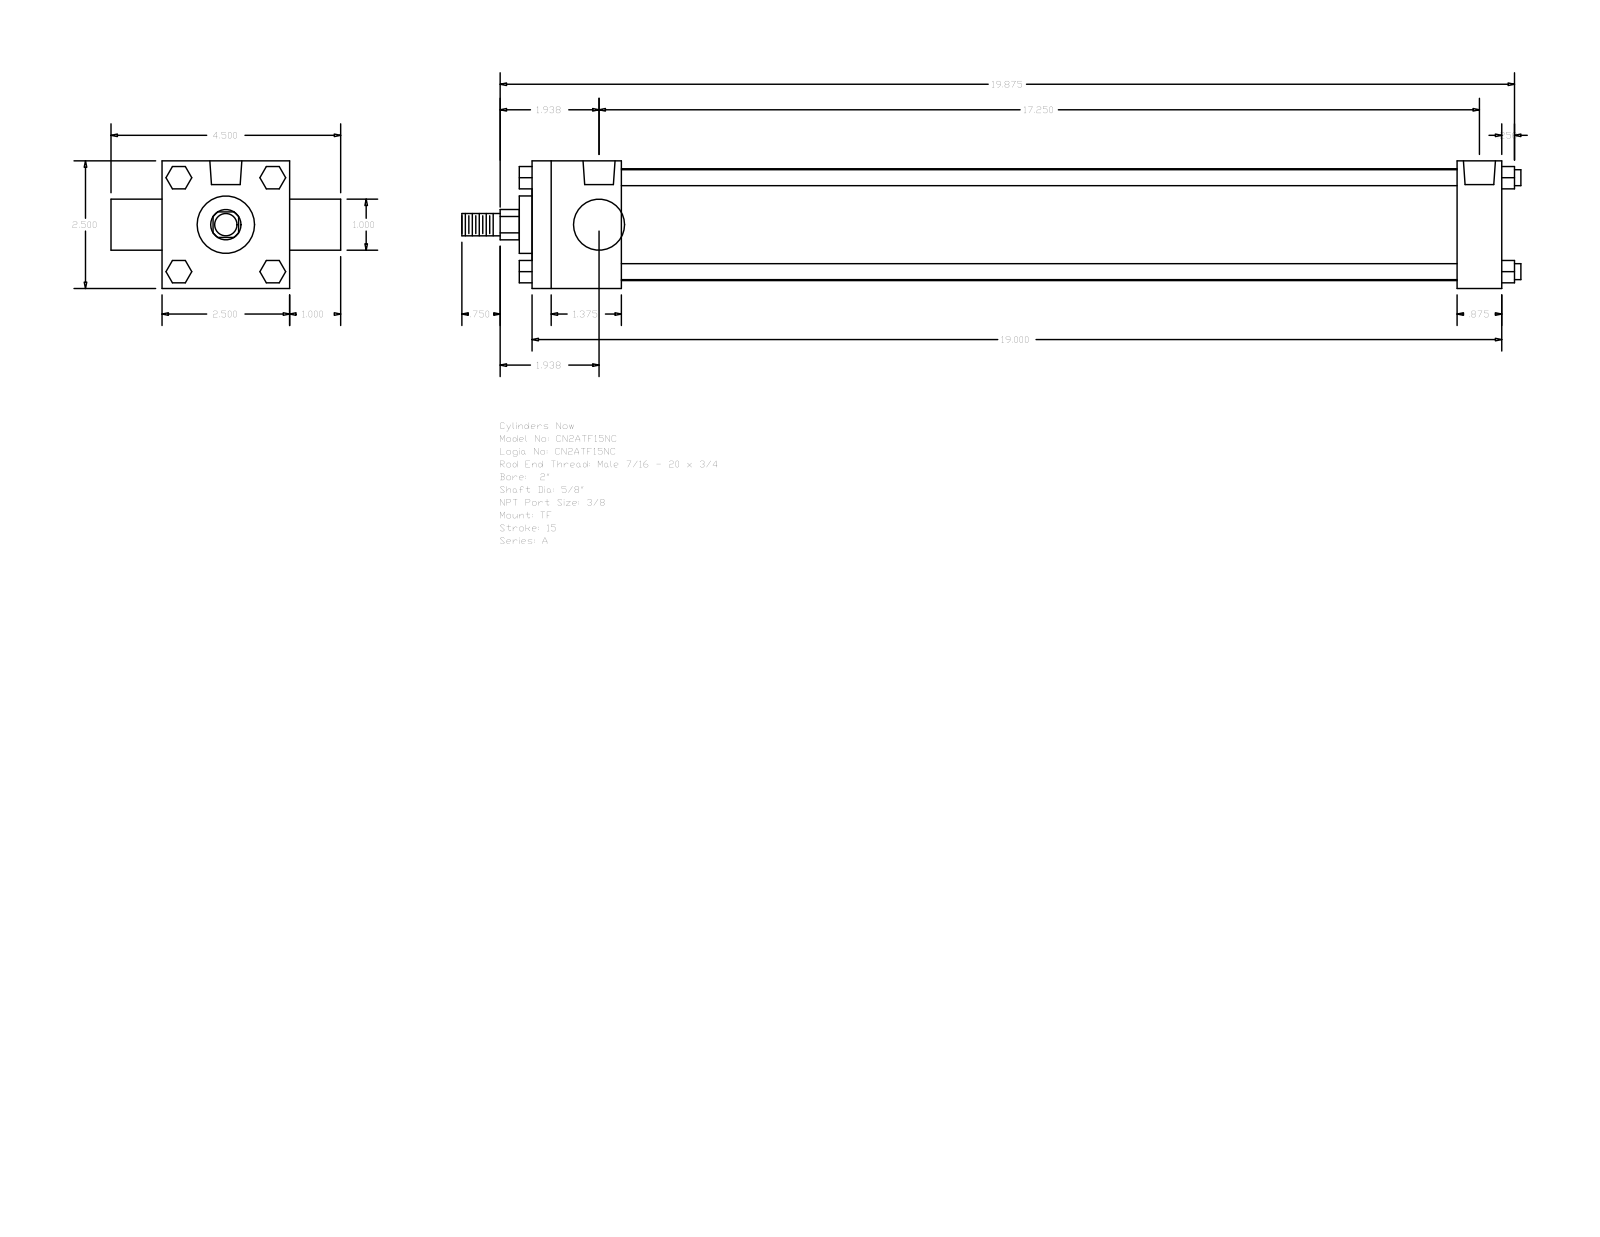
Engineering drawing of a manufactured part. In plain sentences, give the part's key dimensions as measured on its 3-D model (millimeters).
The part is named "A_TF__0200_0.625". Its 3-D file was written by "GSSL Pune (CONFIG_CONTROL_DESIGN)". It is 0 solids with 120 faces: 92 planar, 28 cylindrical and 0 other. Overall it measures 527.05 by 114.3 by 63.5 millimeters. Round holes: 3 of diameter 5.56, 2 of diameter 15.93. Round bosses or shafts: 4 of diameter 7.94, 1 of diameter 55.63, 1 of diameter 28.57, 1 of diameter 25.4, 1 of diameter 15.88, 1 of diameter 11.11. Partial cylindrical surfaces (rounded edges, fillets, slot ends): 1 of radius 7.54. The main face-to-face distances are 63.5, 482.6, 44.45, 460.37, 415.92, 438.15, 22.23, 25.4, 88.9, 50.8. The hole center spacings are 3.97, 3.98, 430.2, 434.17, 434.18, 438.15.
